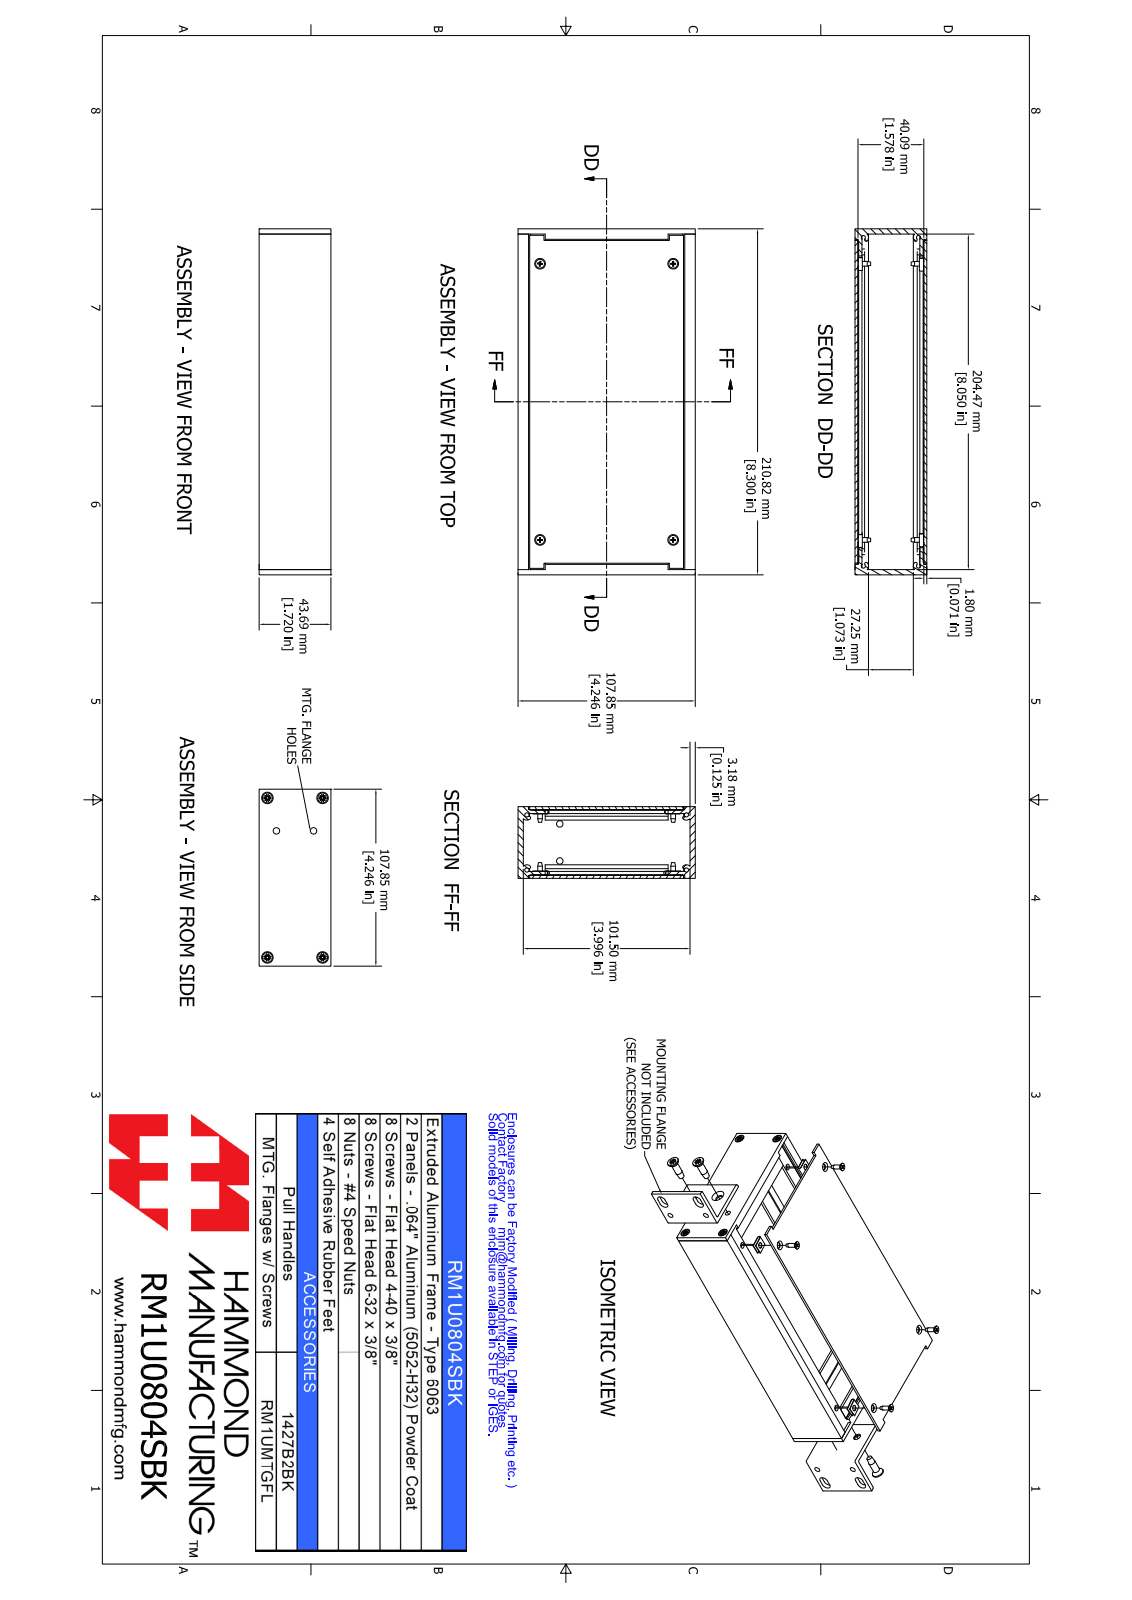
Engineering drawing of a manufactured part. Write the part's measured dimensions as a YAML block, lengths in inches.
part_name: "RM1U0804SBK"
step_written_by: "SolidWorks 2021 (AUTOMOTIVE_DESIGN)"
units: inches
bodies: {solids: 30, faces: 804, planar: 396, cylindrical: 120, other: 288}
overall_size: [8.3, 4.246, 1.72]
volume: 12.41
surface_area: 278.7
round_holes:
  - {diameter: 0.098, count: 4}
  - {diameter: 0.138, count: 4}
  - {diameter: 0.157, count: 4}
  - {diameter: 0.169, count: 4}
  - {diameter: 0.156, count: 2}
round_bosses_or_shafts:
  - {diameter: 0.238, count: 4}
  - {diameter: 0.214, count: 4}
  - {diameter: 0.138, count: 4}
  - {diameter: 0.112, count: 4}
partial_cylinders:
  - {radius: 0.039, count: 8}
  - {radius: 0.049, count: 8}
  - {radius: 0.05, count: 8}
  - {radius: 0.125, count: 8}
  - {radius: 0.038, count: 7}
  - {radius: 0.037, count: 4}
face_to_face_distances: [0.071, 1.649, 1.72, 1.578, 0.125, 4.121, 1.482, 0.167, 1.553, 0.096]
hole_center_spacings: [0.819, 1.323, 3.044, 3.191, 3.231, 3.826, 4.049, 6.625]
